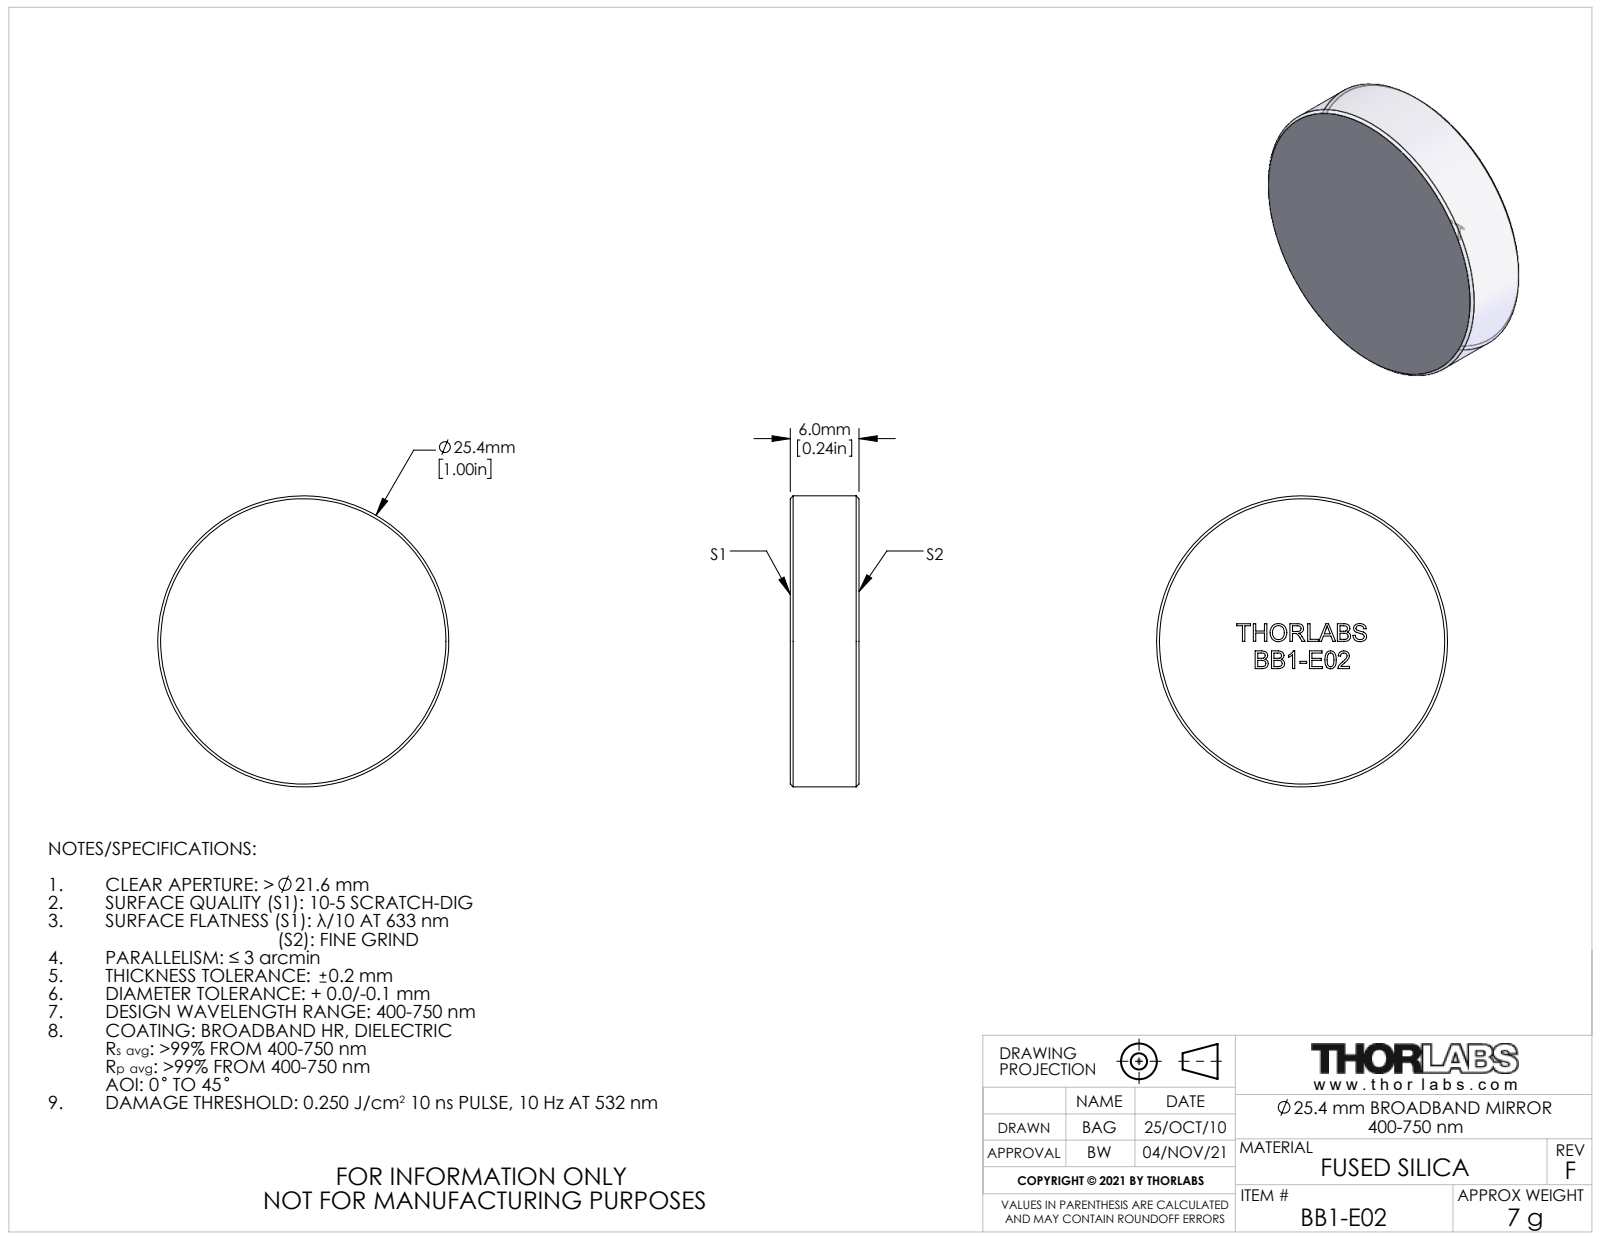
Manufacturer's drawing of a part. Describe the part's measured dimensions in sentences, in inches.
The part is named "3541-E0W". Its 3-D file was written by "SolidWorks 2016 (CONFIG_CONTROL_DESIGN)". It is 1 solid with 218 faces: 129 planar, 2 cylindrical and 87 other. Overall it measures 1 by 1 by 0.236 inches. Its volume is 0.185 cubic inches and its surface area 2.277 square inches. Round bosses or shafts: 1 of diameter 1. The main face-to-face distances are 0.236, 0.093, 0.061, 0.147, 0.054, 0.187, 0.163, 0.076, 0.126, 0.033.
